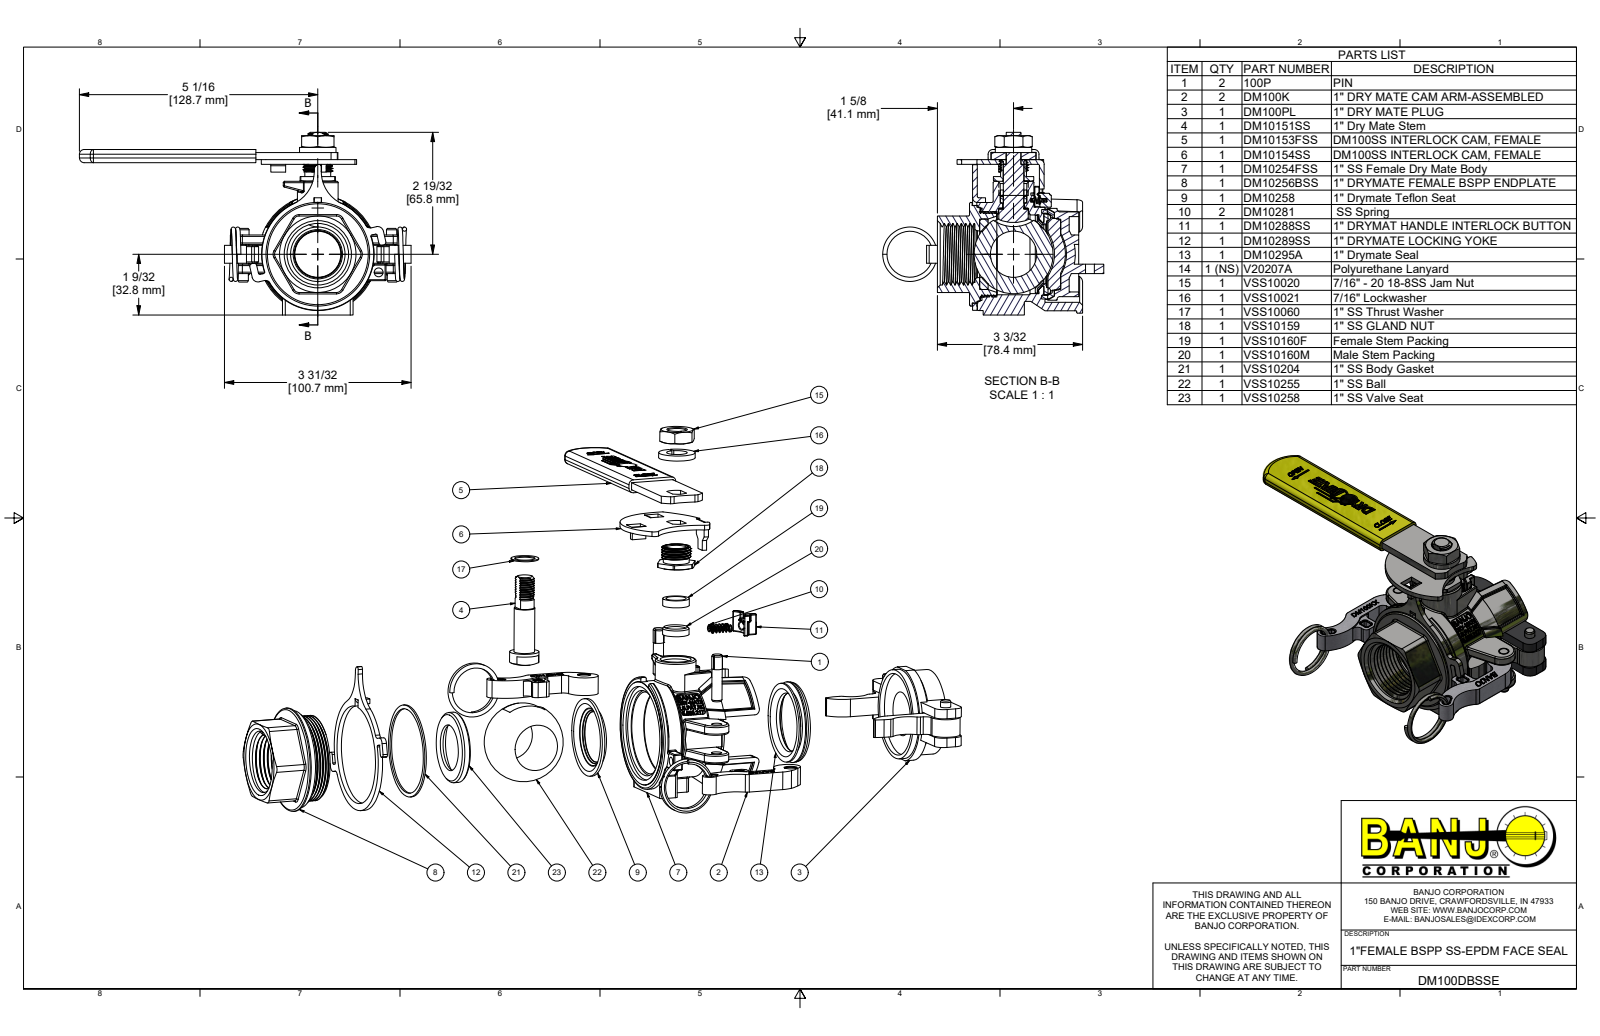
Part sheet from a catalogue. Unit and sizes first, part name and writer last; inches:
Units: inches
Overall size (bounding box): 7.048 × 4.698 × 3.879
Round holes (diameter × count): ⌀0.125 ×3, ⌀0.218 ×2, ⌀0.219 ×2, ⌀0.225 ×2, ⌀0.228 ×2, ⌀0.245 ×2, ⌀0.187 ×1, ⌀0.188 ×1, ⌀0.383 ×1, ⌀0.432 ×1, ⌀0.434 ×1, ⌀0.438 ×1
Round bosses / shafts (diameter × count): ⌀0.227 ×4, ⌀0.217 ×4, ⌀0.22 ×3, ⌀0.01 ×2, ⌀2.39 ×1, ⌀2.2 ×1, ⌀2.07 ×1, ⌀2 ×1
Partial cylindrical surfaces — rounded edges, fillets, slot ends (radius × count): R0.03 ×69, R0.016 ×50, R0.02 ×27, R0.1 ×21, R0.125 ×14, R0.04 ×8, R0.06 ×8, R0.09 ×8
Main face-to-face distances: 0.065, 0.155, 0.215, 0.06, 0.15, 0.22, 0.6, 0.22, 0.2, 0.02
Hole centre spacings: 0.621, 1.076, 0.796, 1.609, 1.662, 1.902, 2.078, 3.253
Volume: 12.14 in³ · Surface area: 198.1 in²
Bodies: 37 solids, 2918 faces (1244 planar, 628 cylindrical, 1046 other)
Part name (STEP PRODUCT): DM100DBSSE; DM10151SS; DM10281; VSS10020 (+8 more)
STEP written by: Autodesk Inventor 2022 (AUTOMOTIVE_DESIGN)
